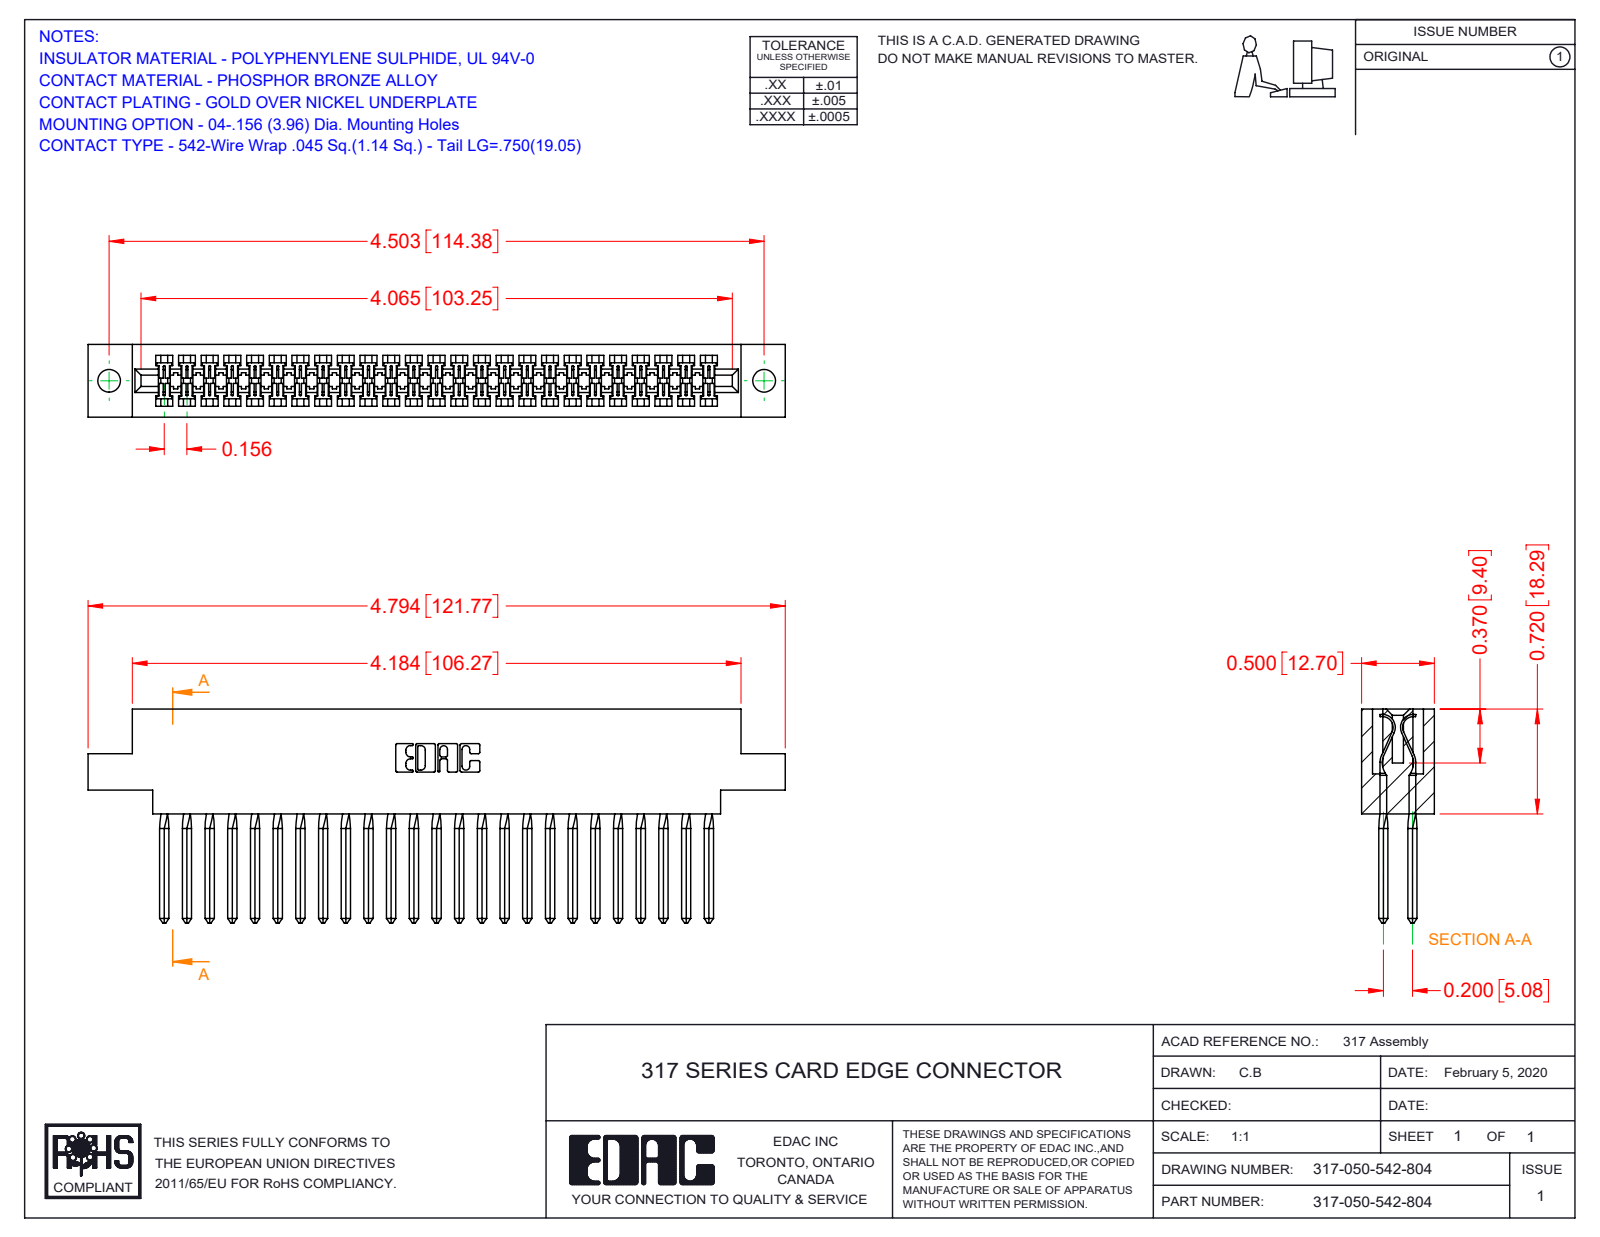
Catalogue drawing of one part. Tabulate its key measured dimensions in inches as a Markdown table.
| quantity | value |
| --- | --- |
| part name | 317-290-003_542; 317 Part_.156 Dia - TH; 317-050-542-804 |
| STEP written by | SolidWorks 2016 (CONFIG_CONTROL_DESIGN) |
| units | inches |
| bodies | 51 solids, 2952 faces (2358 planar, 394 cylindrical, 200 other) |
| overall size | 4.794 × 1.47 × 0.5 |
| volume | 1.179 in³ |
| surface area | 40.5 in² |
| round holes (diameter × count) | 0.156 × 2 |
| partial cylindrical surfaces (radius × count) | 0.006 × 100, 0.01 × 22, 0.007 × 6, 0.031 × 6, 0.026 × 3, 0.074 × 2, 0.089 × 2, 0.1 × 2 |
| main face-to-face distances | 0.5, 0.075, 0.425, 0.35, 0.2, 0.11, 0.116, 0.046, 0.136, 0.72 |
| hole center spacings | 4.503 |
